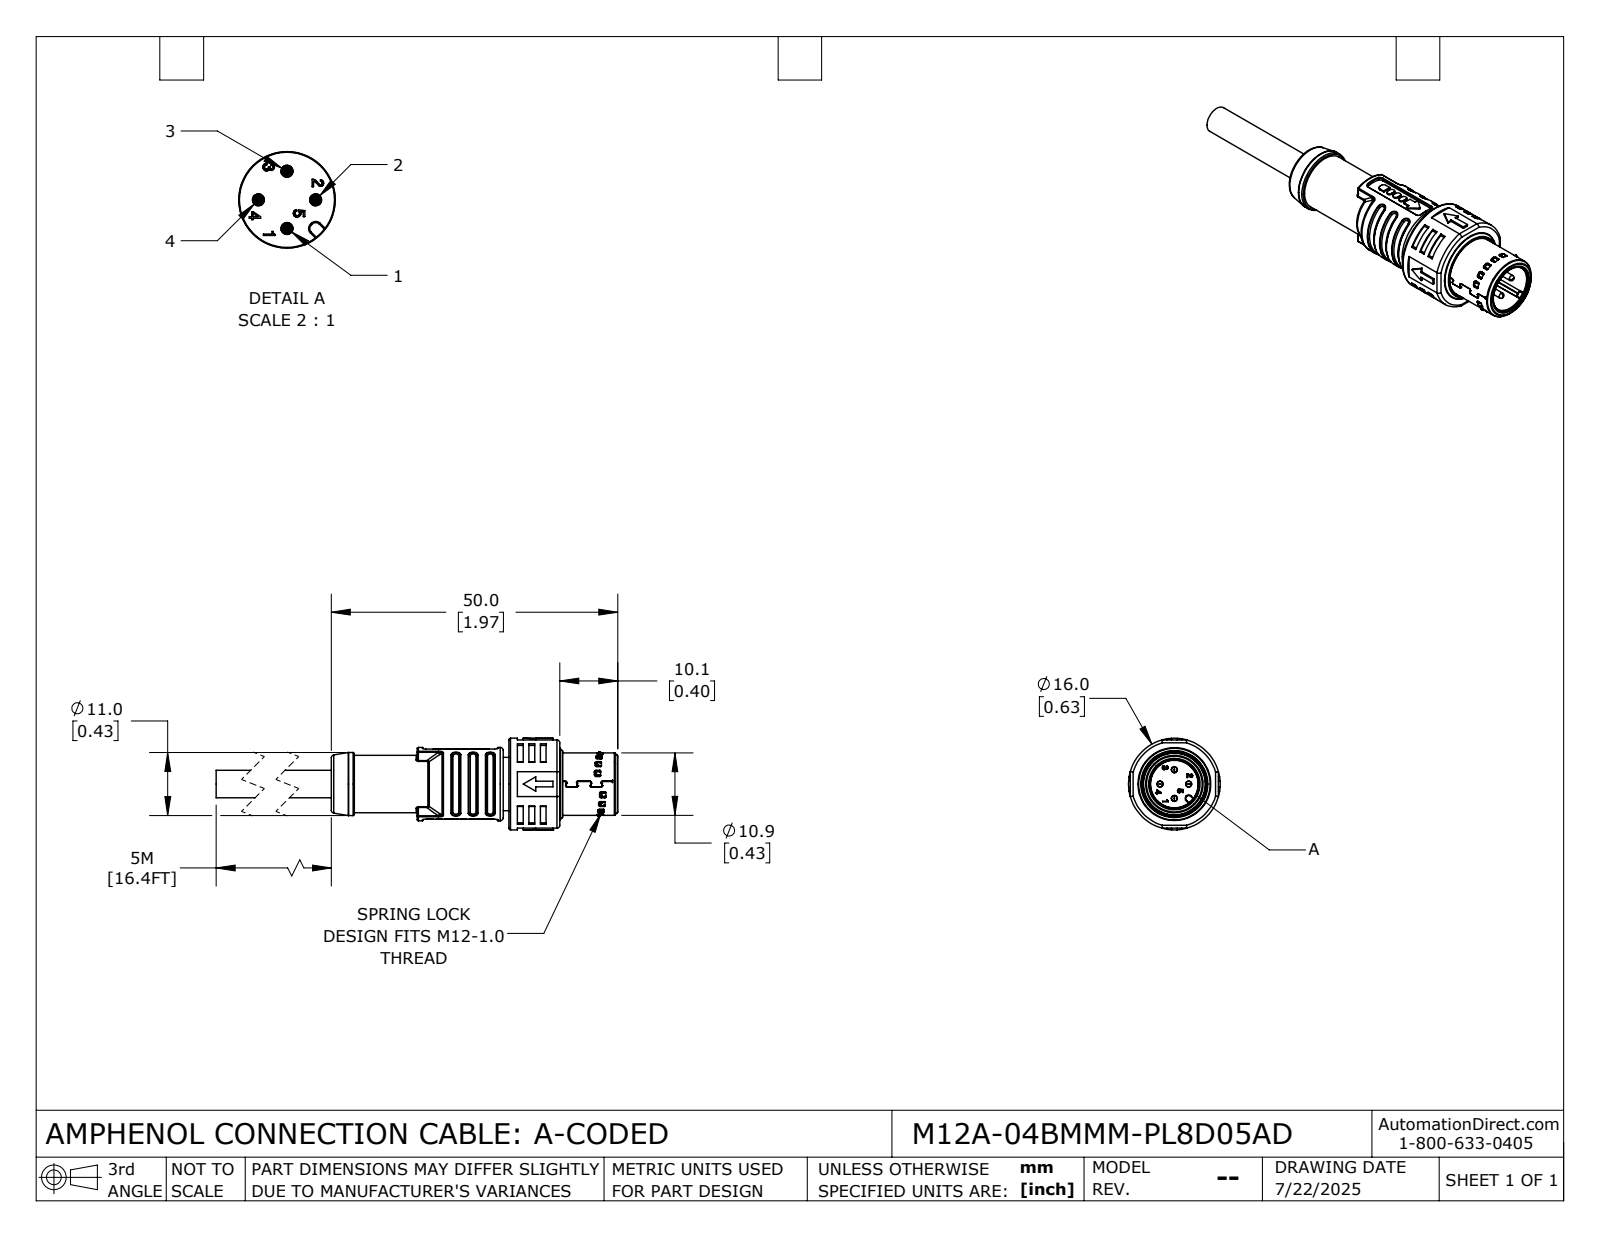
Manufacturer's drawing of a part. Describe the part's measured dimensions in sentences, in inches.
The part is named "M12A-04BMMM-PL8D05AD". Its 3-D file was written by "SolidWorks 2024 (CONFIG_CONTROL_DESIGN)". It is 1 solid with 2276 faces: 1081 planar, 672 cylindrical and 523 other. Overall it measures 2.862 by 0.63 by 0.63 inches. Its volume is 0.316 cubic inches and its surface area 9.253 square inches. Round holes: 4 of diameter 0.041, 4 of diameter 0.057, 1 of diameter 0.327, 1 of diameter 0.354, 1 of diameter 0.4, 1 of diameter 0.413, 1 of diameter 0.453, 1 of diameter 0.465, 1 of diameter 0.559. Round bosses or shafts: 4 of diameter 0.055, 4 of diameter 0.039, 1 of diameter 0.63, 1 of diameter 0.555, 1 of diameter 0.504, 1 of diameter 0.488, 1 of diameter 0.433, 1 of diameter 0.429. Partial cylindrical surfaces (rounded edges, fillets, slot ends): 114 of radius 0.008, 66 of radius 0.01, 64 of radius 0.012, 44 of radius 0.006, 38 of radius 0.02, 12 of radius 0.005, 11 of radius 0.028, 10 of radius 0.004. The main face-to-face distances are 0.039, 0.398, 0.35, 0.339, 0.098, 0.059, 0.047, 1.28, 0.606, 1.618. The hole center spacings are 0.098, 0.139, 0.197.
